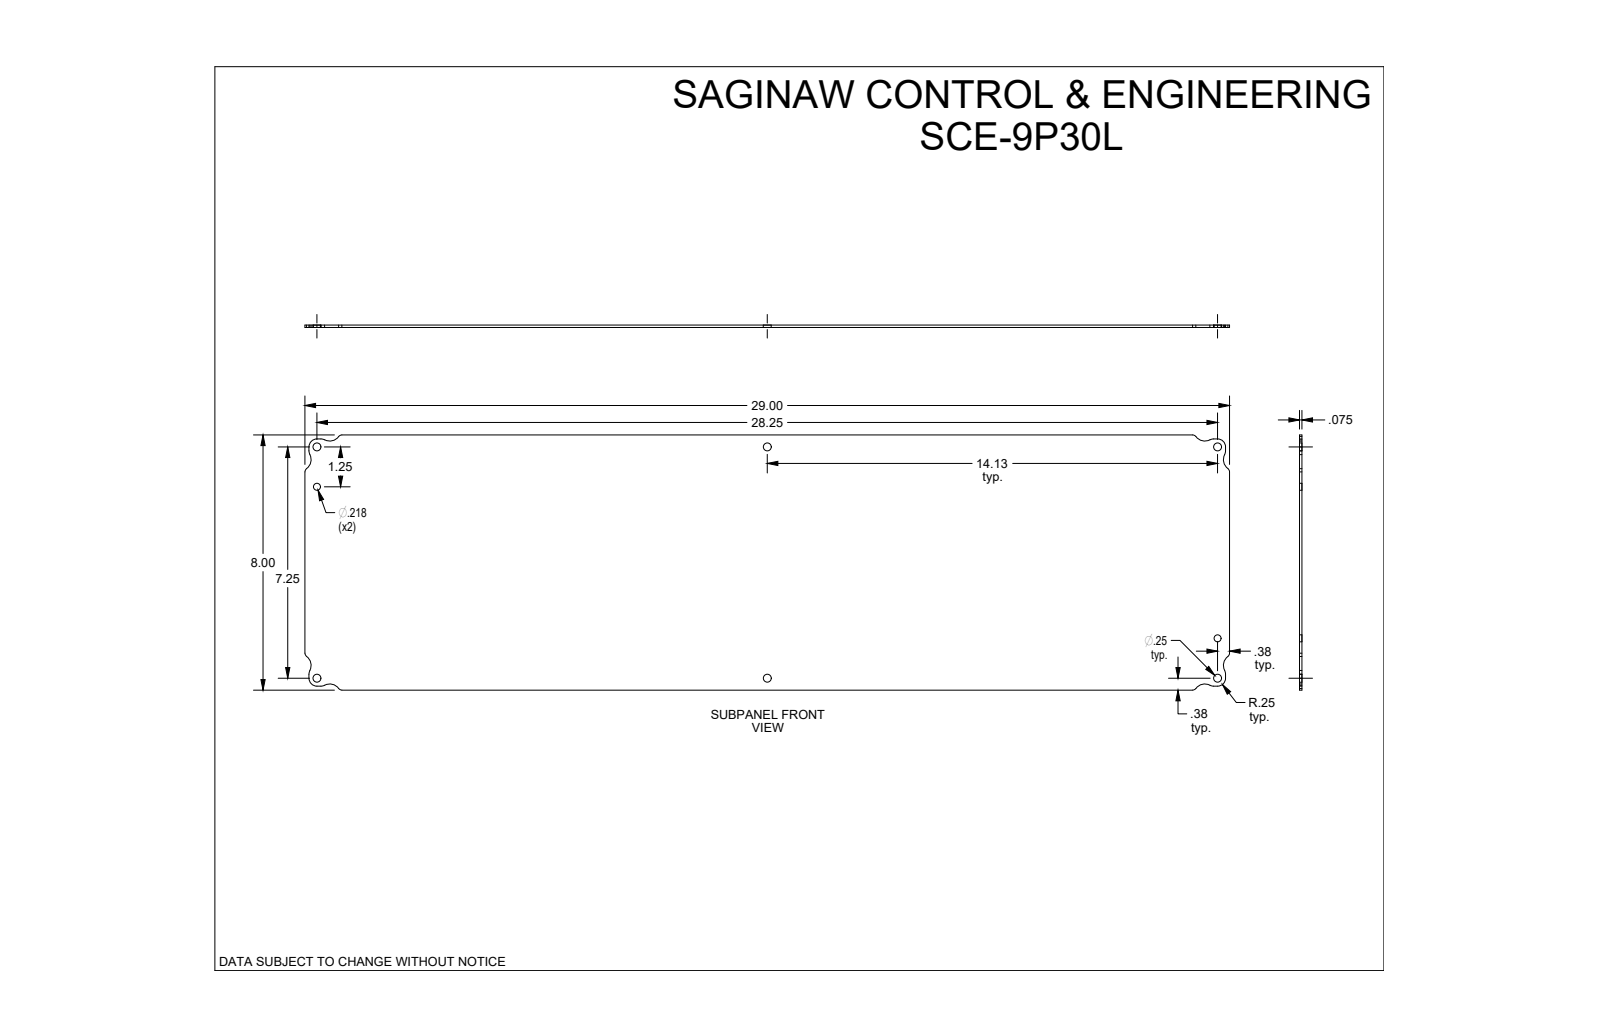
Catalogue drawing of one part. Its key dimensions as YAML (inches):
part_name: "SCE-9P30L"
step_written_by: "SolidWorks 2019 (CONFIG_CONTROL_DESIGN)"
units: inches
bodies: {solids: 1, faces: 50, planar: 14, cylindrical: 36, other: 0}
overall_size: [29, 8, 0.075]
volume: 17.28
surface_area: 466.8
round_holes:
  - {diameter: 0.25, count: 6}
  - {diameter: 0.218, count: 2}
partial_cylinders:
  - {radius: 0.25, count: 12}
  - {radius: 0.125, count: 8}
  - {radius: 0.344, count: 8}
face_to_face_distances: [0.075, 8, 29, 0.125, 7.875, 28.875, 7.75, 28.75]
hole_center_spacings: [14.125, 15.877, 7.25, 1.25, 6, 14.18, 15.346, 28.25]
